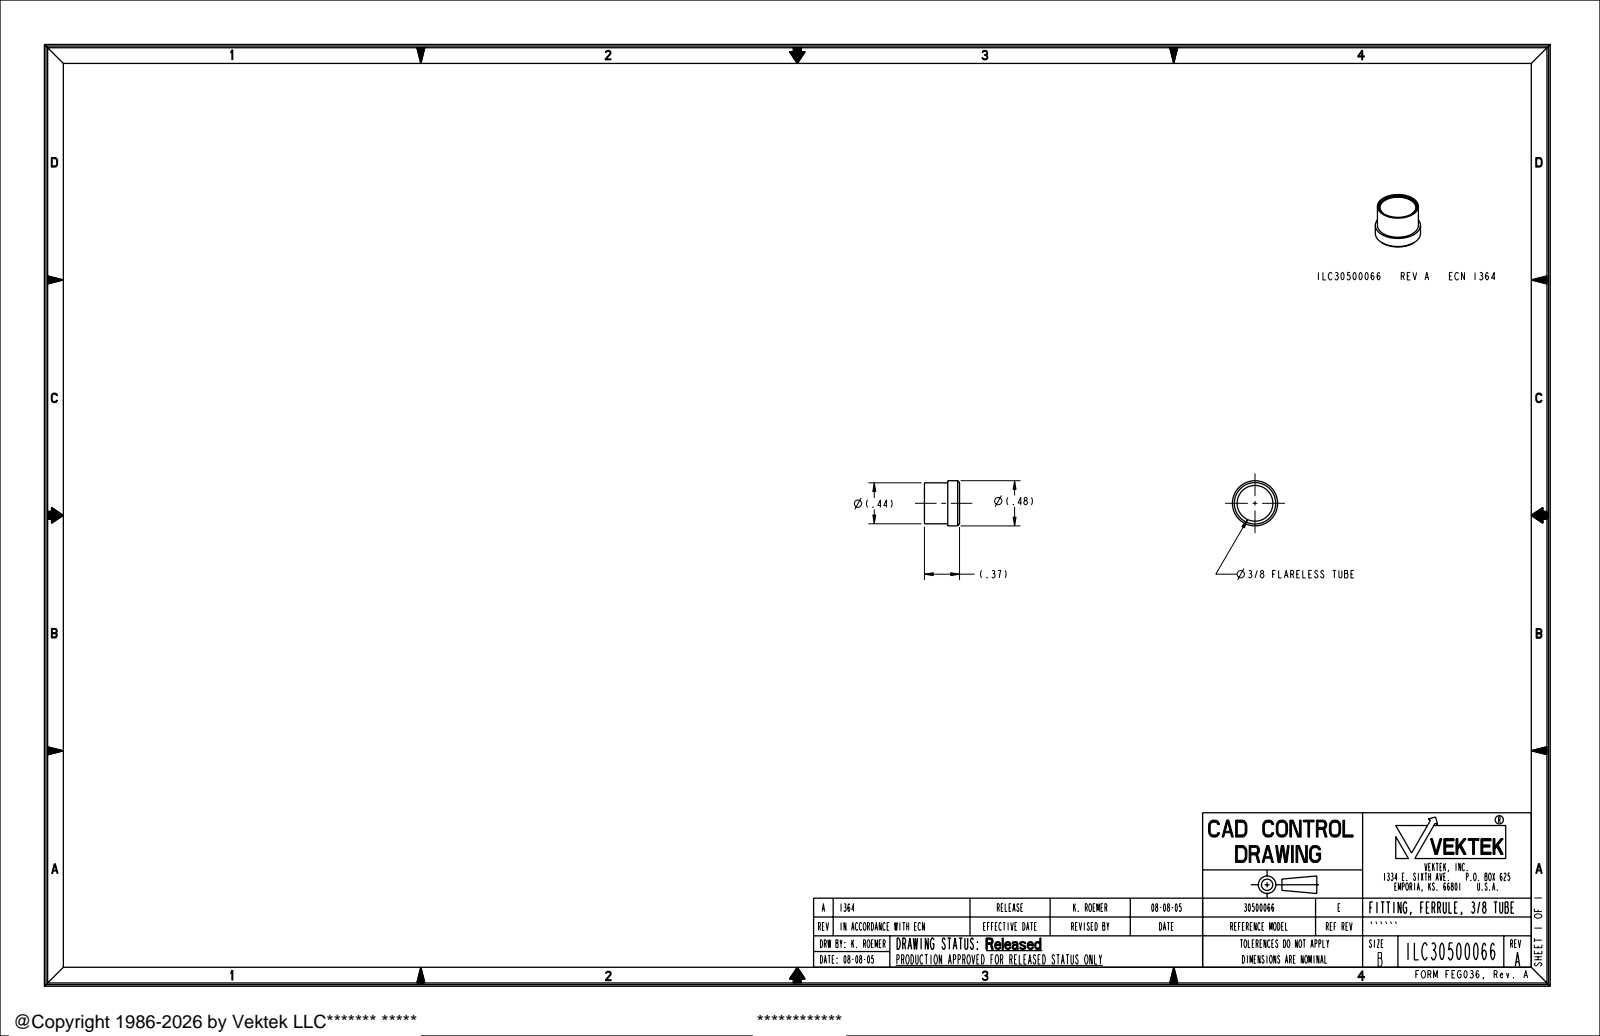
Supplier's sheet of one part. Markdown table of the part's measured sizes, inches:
| quantity | value |
| --- | --- |
| part name | ILC30500066 |
| STEP written by | PRO/ENGINEER BY PARAMETRIC TECHNOLOGY CORPORATION, 2004290 (AUTOMOTIVE_DESIGN_CC2) |
| units | inches |
| bodies | 1 solid, 14 faces (4 planar, 8 cylindrical, 2 other) |
| overall size | 0.48 × 0.48 × 0.373 |
| volume | 0.017 in³ |
| surface area | 1.091 in² |
| round holes (diameter × count) | 0.38 × 1, 0.405 × 1 |
| round bosses / shafts (diameter × count) | 0.48 × 1, 0.435 × 1 |
| main face-to-face distances | 0.125, 0.373, 0.248, 0.358, 0.233, 0.015 |
